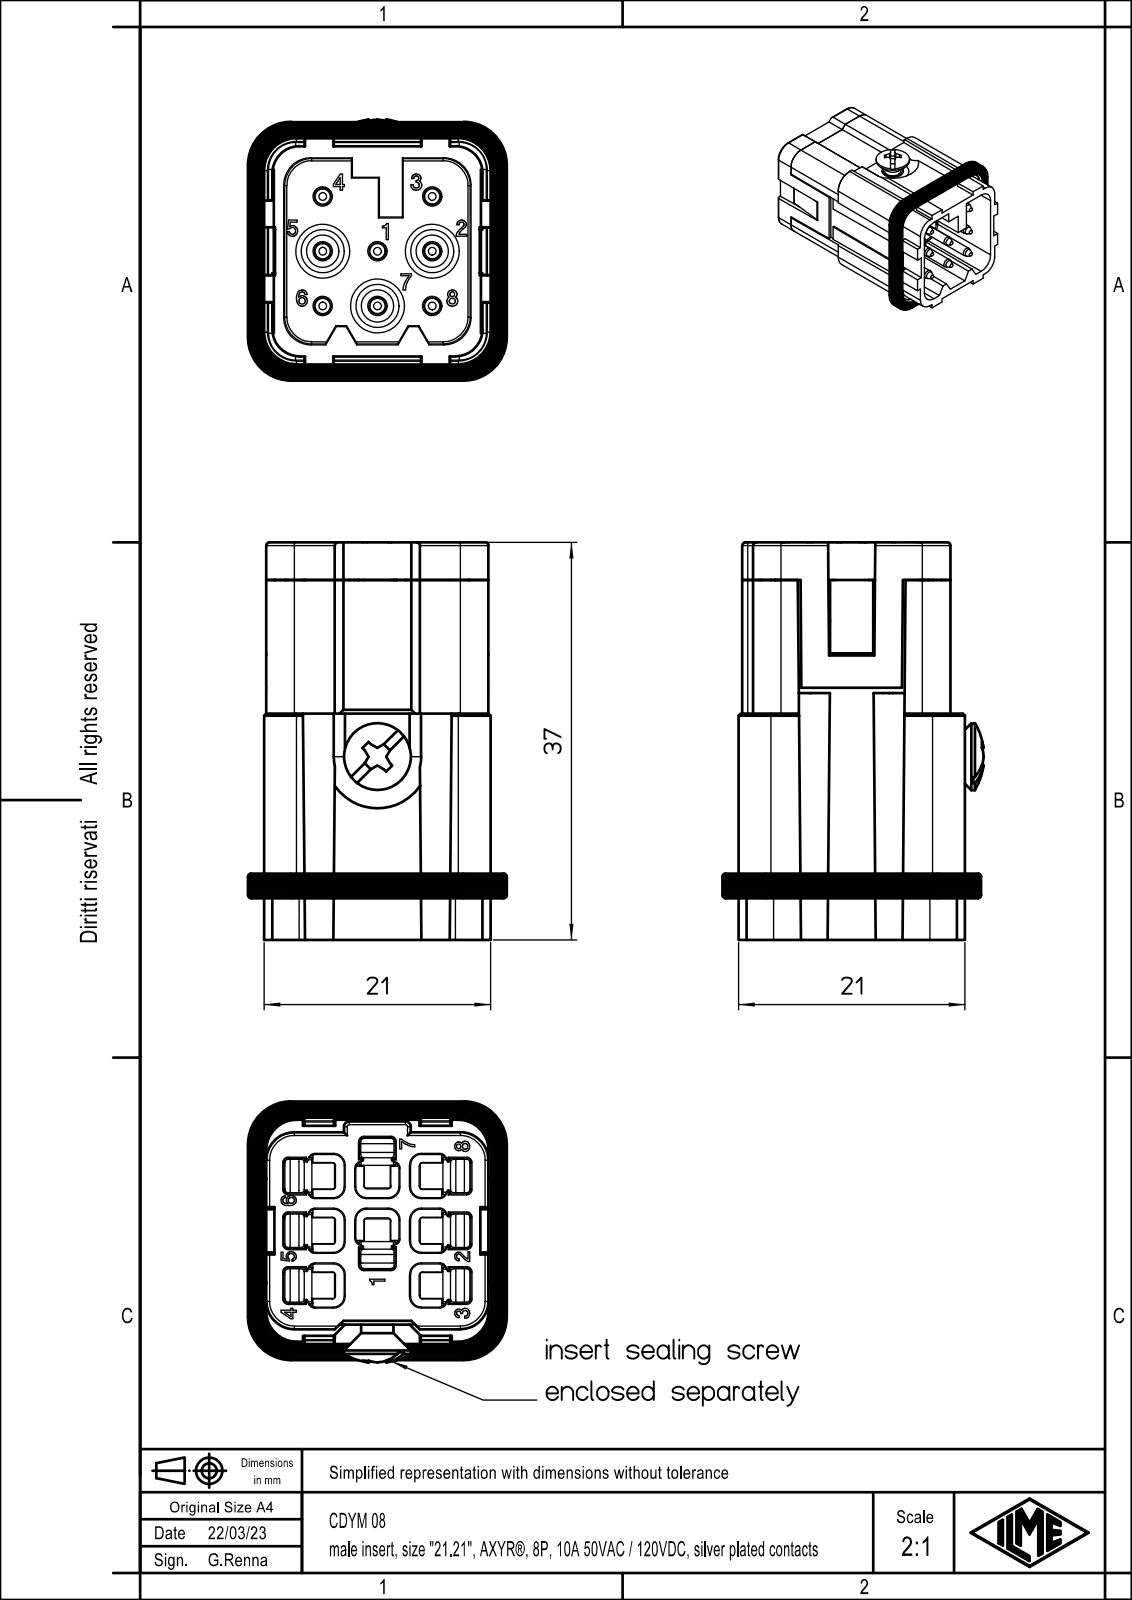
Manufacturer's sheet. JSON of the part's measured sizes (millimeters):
{"part_name": "CDYM 08", "step_written_by": "Creo Elements/Direct Modeling 20.1B 02-Apr-2019 (C) Parametric Technology GmbH (AUTOMOTIVE_DESIGN)", "units": "millimeters", "bodies": {"solids": 1, "faces": 1433, "planar": 828, "cylindrical": 394, "other": 211}, "overall_size": [36.9, 24.22, 24], "volume_mm3": 10637, "surface_area_mm2": 7899, "round_holes": [[1.8, 8], [2.5, 1], [4, 1]], "round_bosses_or_shafts": [[1.6, 8], [4, 3], [6.2, 1], [3.8, 1], [3, 1]], "partial_cylinders_radius": [[0.1, 58], [0.3, 55], [0.5, 34], [0.2, 30], [0.4, 16], [1, 16], [2.5, 8], [1.5, 4]], "face_to_face_distances": [0.75, 20.25, 20.05, 0.8, 19.3, 19.5, 1, 19.8, 0.6, 19.65], "hole_center_spacings": [5.08, 7.18, 11.36, 10.16, 14.37]}
